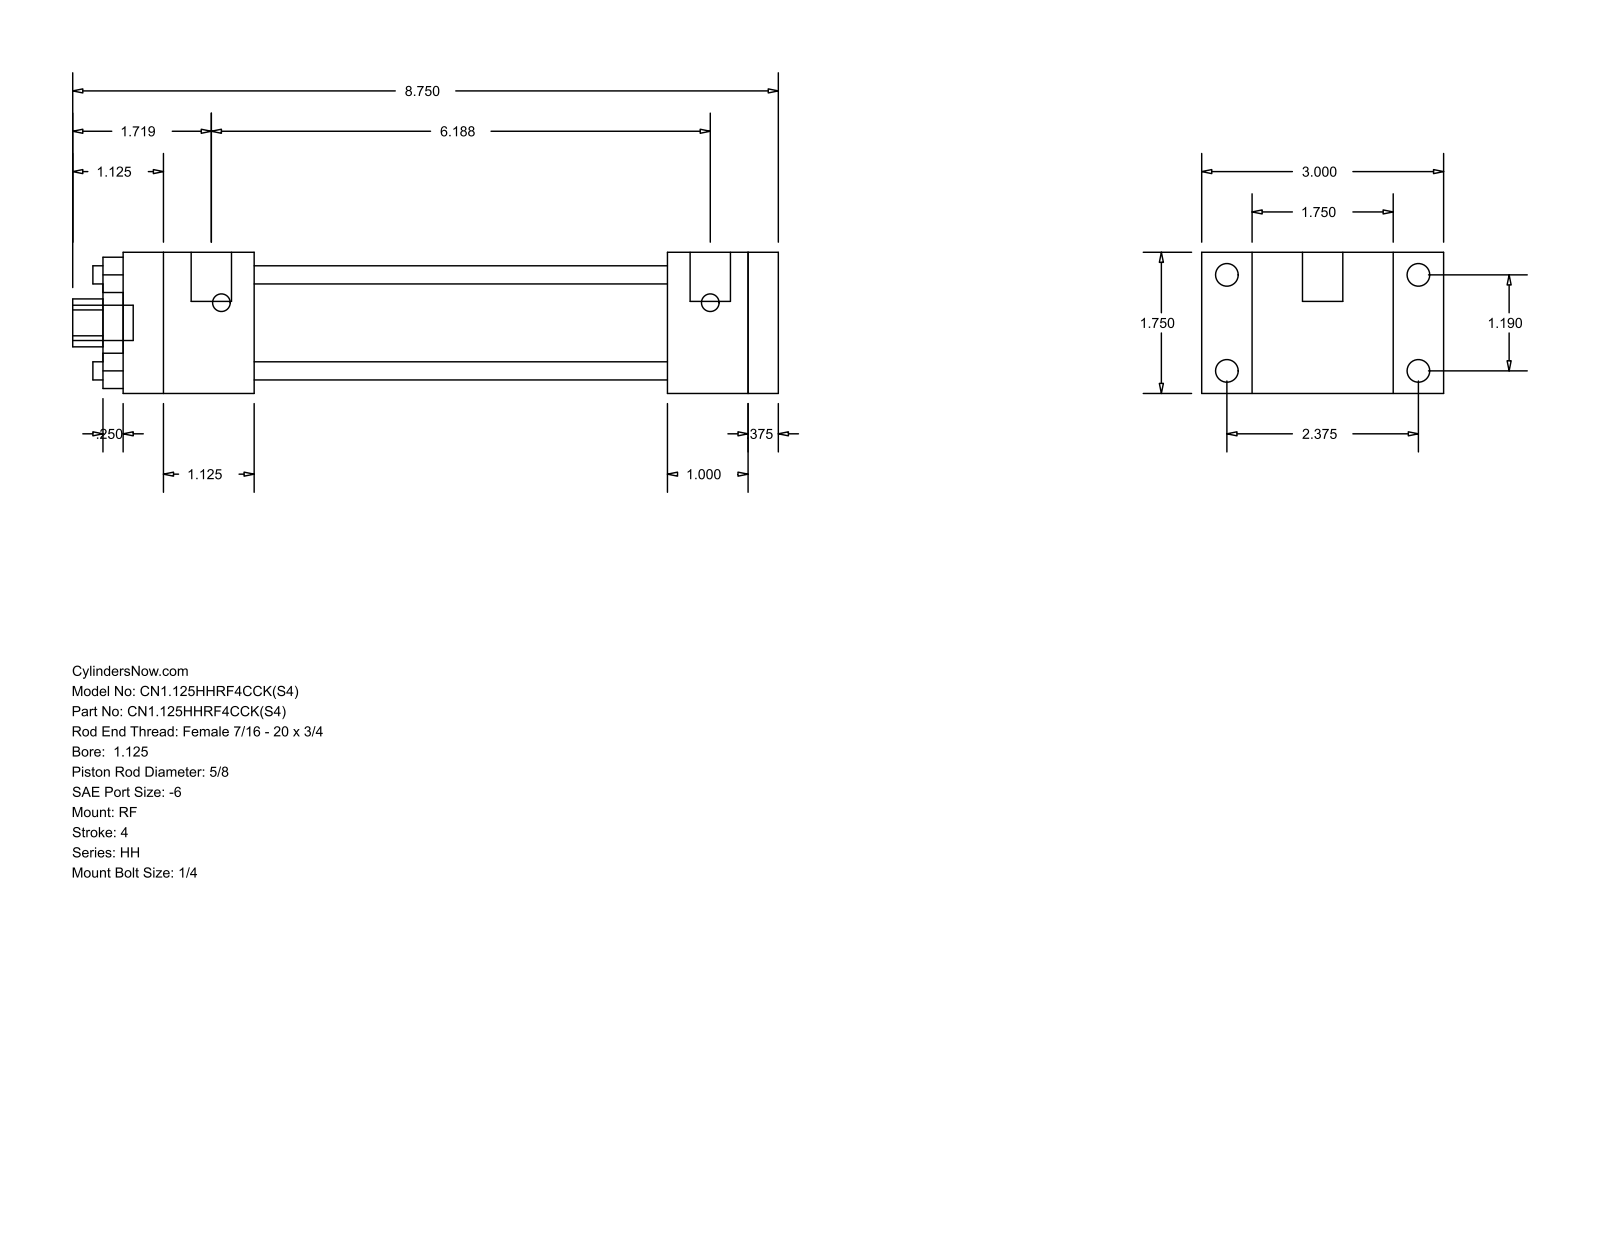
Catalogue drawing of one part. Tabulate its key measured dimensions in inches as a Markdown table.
| quantity | value |
| --- | --- |
| part name | HH_RF__0112_0.625 |
| STEP written by | GSSL Pune (CONFIG_CONTROL_DESIGN) |
| units | inches |
| bodies | 0 solids, 92 faces (64 planar, 28 cylindrical, 0 other) |
| overall size | 8.75 × 3 × 1.75 |
| round holes (diameter × count) | 0.225 × 4, 0.625 × 1, 1.125 × 1, 1.375 × 1 |
| round bosses / shafts (diameter × count) | 0.281 × 4, 0.219 × 4, 0.5 × 2, 0.437 × 1 |
| partial cylindrical surfaces (radius × count) | 0.297 × 1 |
| main face-to-face distances | 1.75, 0.375, 8.125, 0.625, 6.125, 6.5, 5.125, 1, 1.375, 1.625 |
| hole center spacings | 0.841, 1.19, 1.683 |
